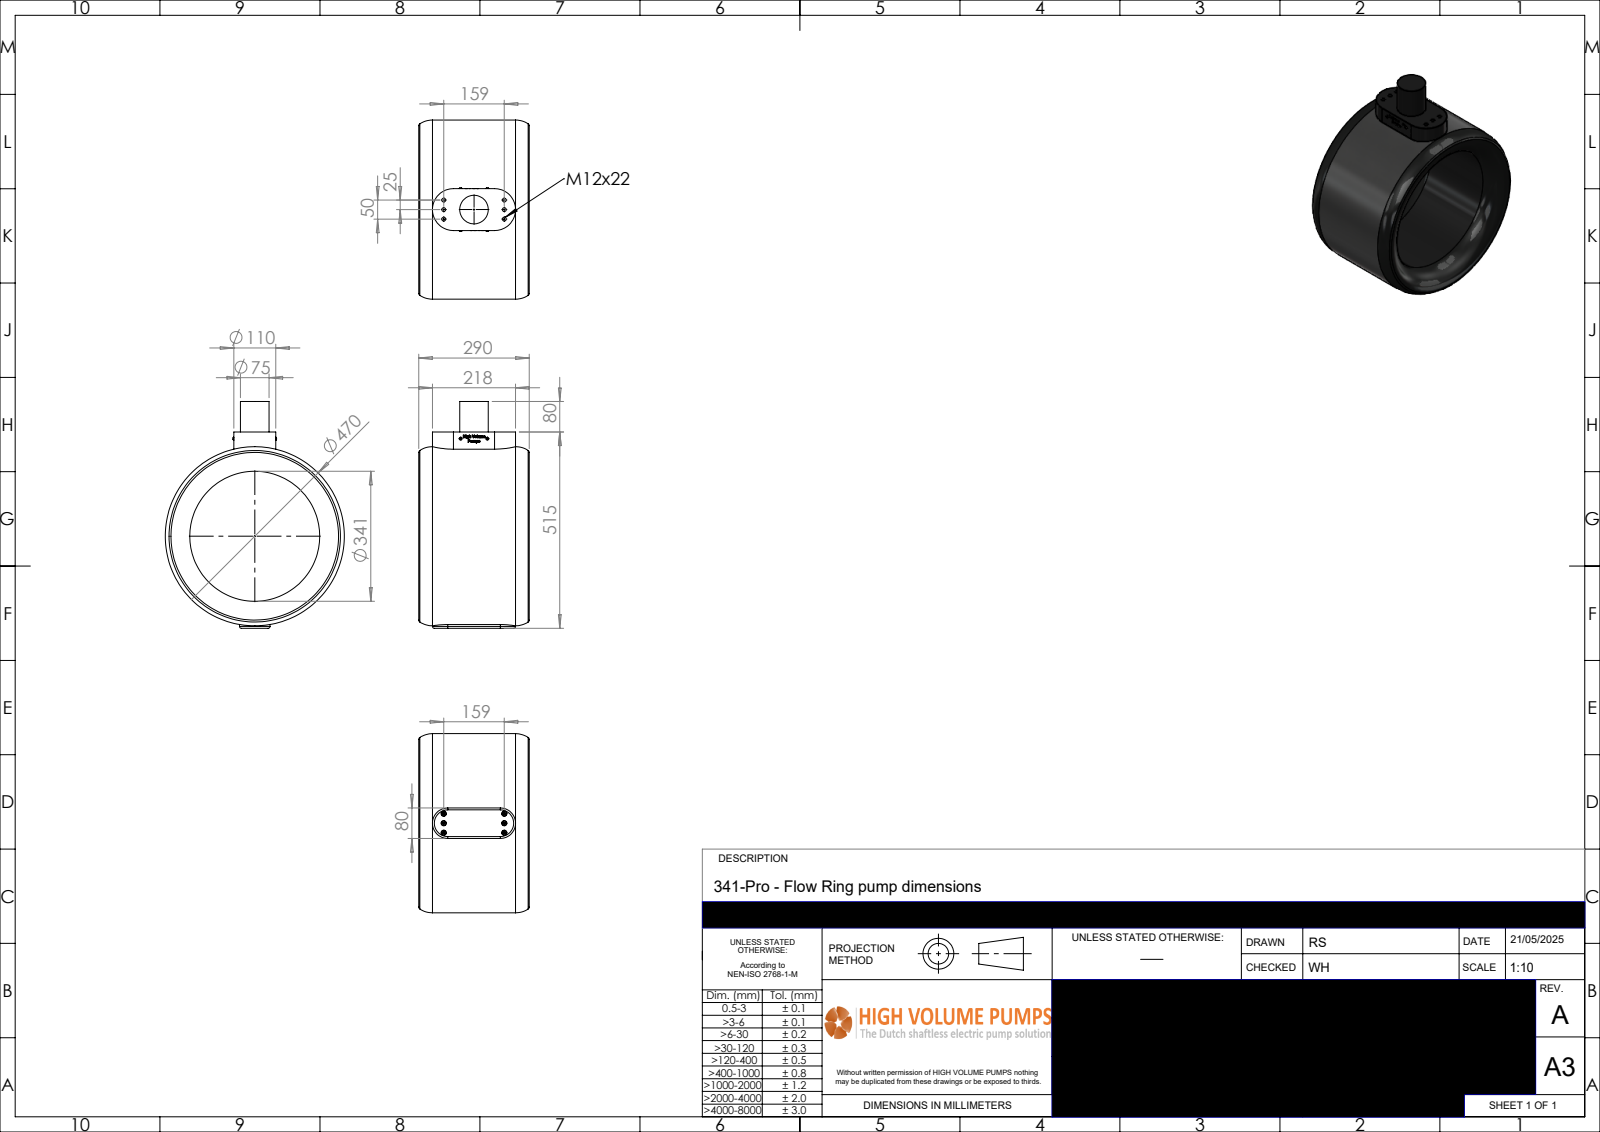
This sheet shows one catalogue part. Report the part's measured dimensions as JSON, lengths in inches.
{"part_name": "P-341-530-rev-A-FR", "step_written_by": "SolidWorks 2024 (AUTOMOTIVE_DESIGN)", "units": "inches", "bodies": {"solids": 1, "faces": 667, "planar": 385, "cylindrical": 44, "other": 238}, "overall_size": [23.427, 18.504, 11.417], "volume_in3": 1436, "surface_area_in2": 1369, "round_holes": [[0.26, 6], [0.402, 6], [13.425, 1]], "round_bosses_or_shafts": [[0.456, 6], [0.236, 6], [0.299, 2], [18.504, 1], [2.953, 1]], "partial_cylinders_radius": [[0.197, 2], [1.575, 2], [2.165, 2]], "face_to_face_distances": [20.277, 3.15, 4.331, 23.427, 0.591, 3.74, 0.02, 4.311, 0.571, 3.72], "hole_center_spacings": [0.984, 6.337, 6.26, 1.969, 6.562]}
